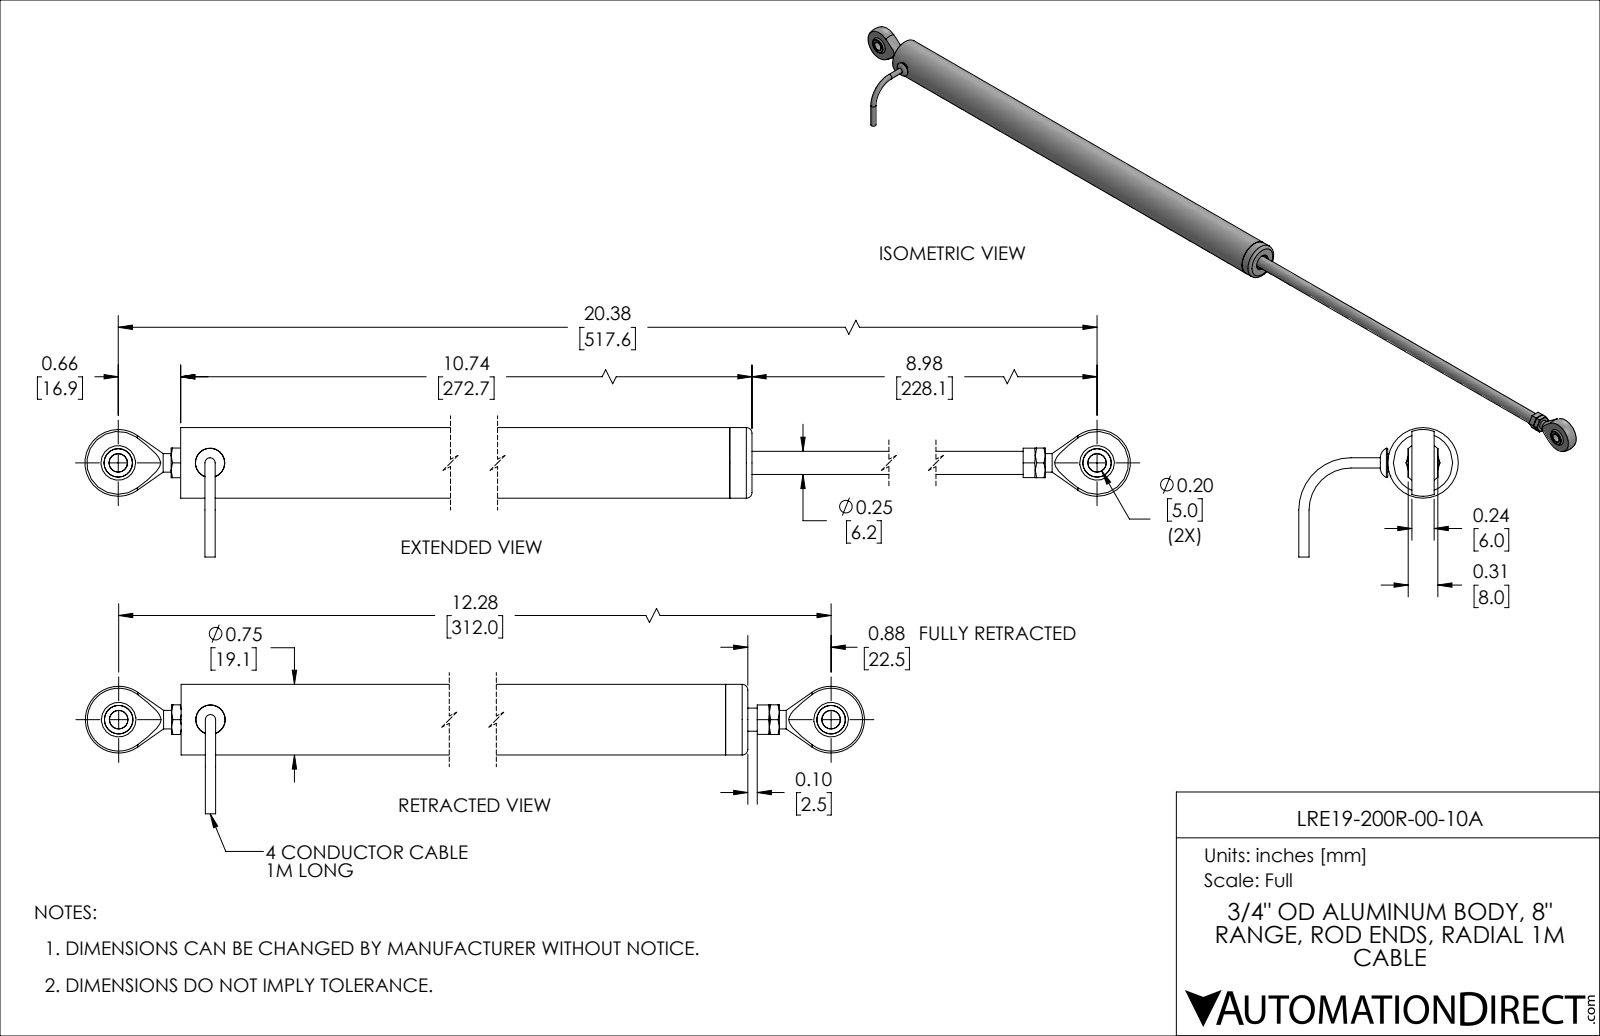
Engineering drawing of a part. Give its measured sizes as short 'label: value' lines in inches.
name: LRE19-200R-00-10A
written by: SolidWorks 2019 (AUTOMOTIVE_DESIGN)
unit: in
bodies: 13 solids, 163 faces (58 planar, 34 cylindrical, 71 other)
size: 12.952 × 1.695 × 1.375
volume: 1.995 in³; area: 70.91 in²
holes: 3× ⌀0.197, 1× ⌀0.109, 1× ⌀0.165, 1× ⌀0.188, 1× ⌀0.193, 1× ⌀0.221, 1× ⌀0.307, 1× ⌀0.62, 1× ⌀0.625, 1× ⌀0.65, 1× ⌀0.71, 1× ⌀0.725
bosses: 1× ⌀0.75, 1× ⌀0.7, 1× ⌀0.624, 1× ⌀0.246, 1× ⌀0.223, 1× ⌀0.218, 1× ⌀0.109
face distances: 0.236, 0.105, 10.626, 10.731, 10.495, 10.39, 0.236, 0.315, 0.039, 0.276
hole spacings: 0.975, 11.309, 12.284
